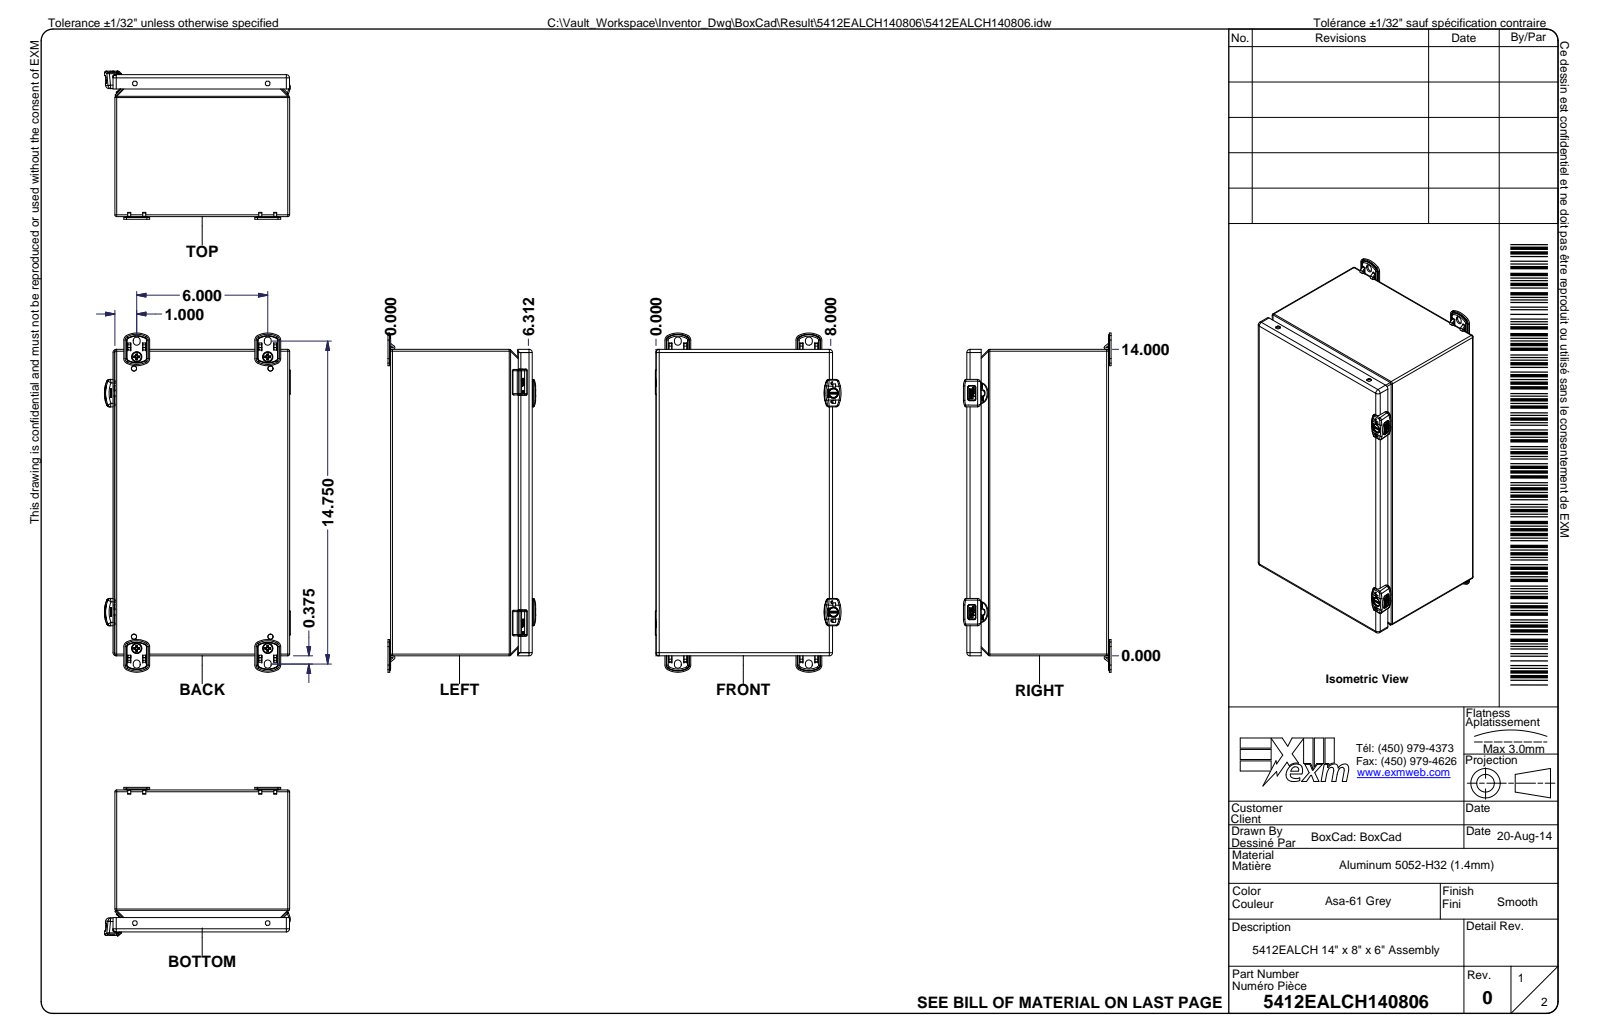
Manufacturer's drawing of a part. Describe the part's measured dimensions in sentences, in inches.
The part is named "5412EALCH140806; 5412EALCH140806B; 5412EALCH140806B-P; STK-A-70469-1 (+8 more)". Its 3-D file was written by "Autodesk Inventor 2020 (AUTOMOTIVE_DESIGN)". It is 59 solids with 8409 faces: 3583 planar, 2002 cylindrical and 2824 other. Overall it measures 15.496 by 8.503 by 6.76 inches. Its volume is 38.73 cubic inches and its surface area 1 382 square inches. Round holes: 4 of diameter 0.165, 4 of diameter 0.173, 4 of diameter 0.197, 4 of diameter 0.197, 4 of diameter 0.236, 4 of diameter 0.236, 4 of diameter 0.32, 2 of diameter 0.03, 2 of diameter 0.175, 2 of diameter 0.201, 2 of diameter 0.24, 2 of diameter 0.339. Round bosses or shafts: 8 of diameter 0.232, 4 of diameter 0.5, 4 of diameter 0.3, 4 of diameter 0.236, 4 of diameter 0.193, 3 of diameter 0.197, 2 of diameter 0.412, 2 of diameter 0.394. Partial cylindrical surfaces (rounded edges, fillets, slot ends): 257 of radius 0.02, 209 of radius 0.01, 92 of radius 0.039, 64 of radius 0.004, 60 of radius 0.008, 57 of radius 0.059, 35 of radius 0.031, 33 of radius 0.005. The main face-to-face distances are 0.053, 7.947, 0.053, 6.433, 6.38, 6.486, 6.433, 13.947, 0.236, 0.304. The hole center spacings are 0.546, 12.781, 12.25, 6.148, 11.17, 13.752, 14.173, 1.506.
